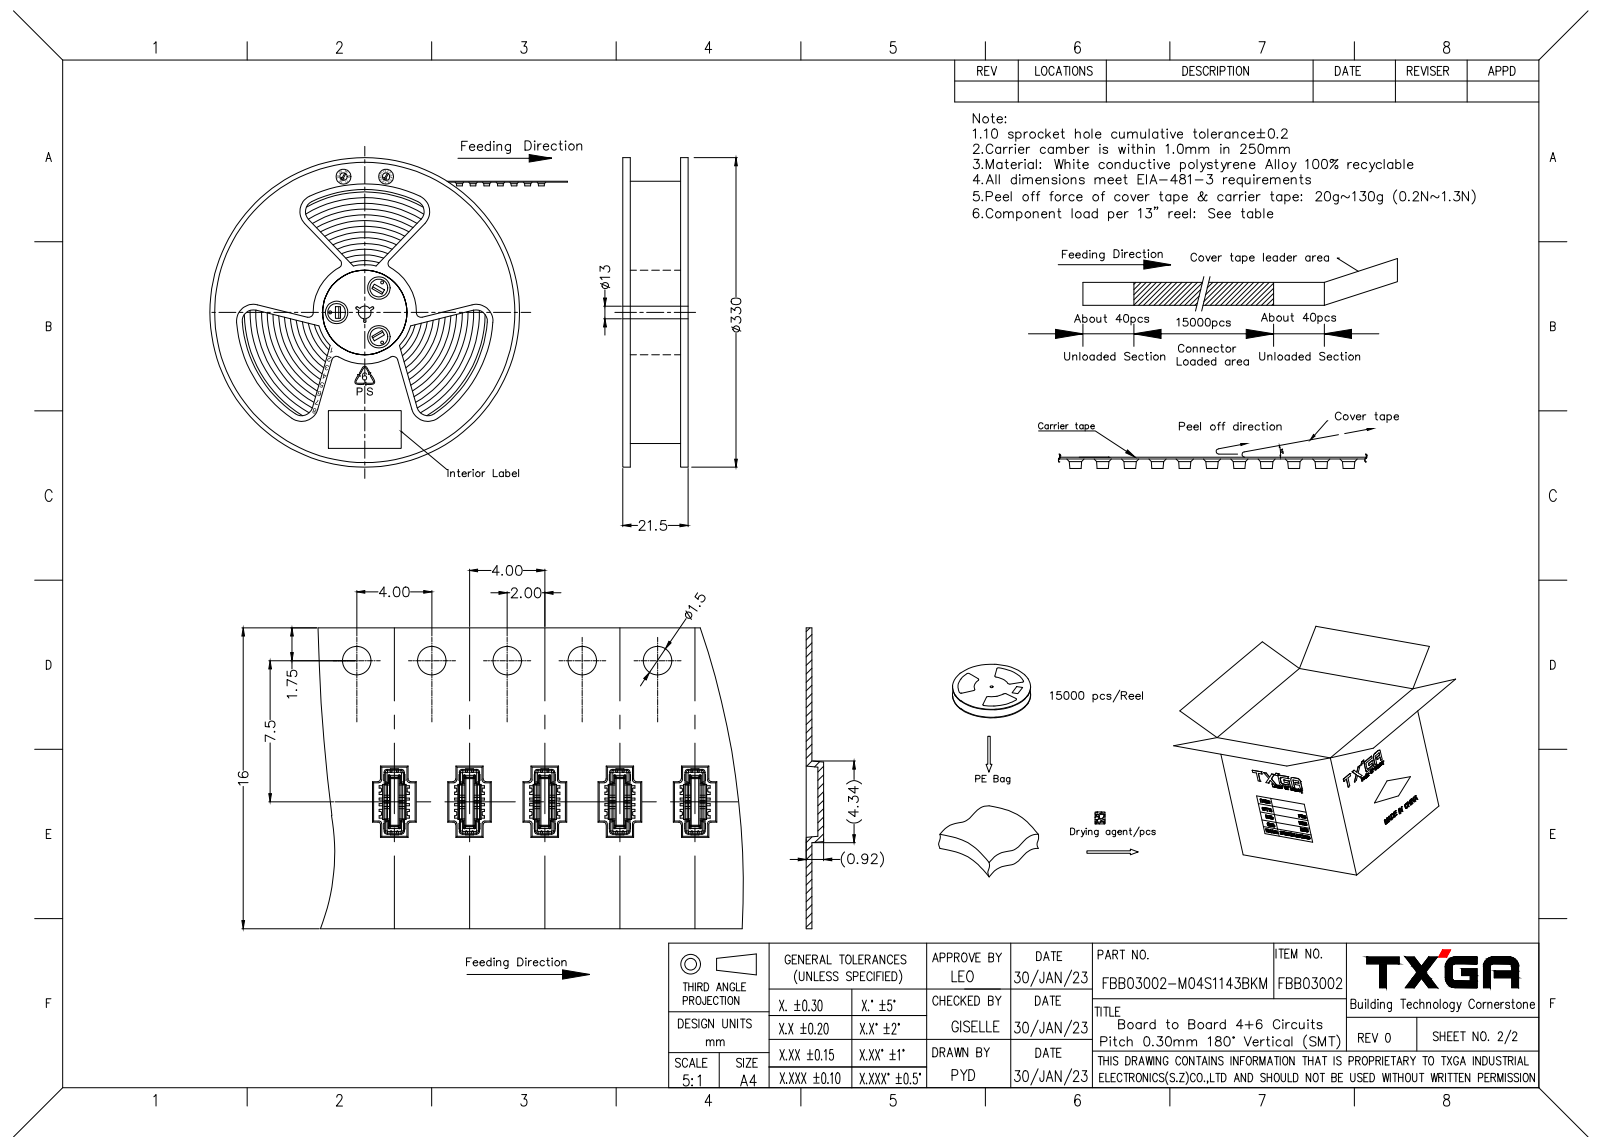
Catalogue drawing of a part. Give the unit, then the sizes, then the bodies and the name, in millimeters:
Units: millimetres
Overall size (bounding box): 3.64 × 1.9 × 0.49
Partial cylindrical surfaces — rounded edges, fillets, slot ends (radius × count): R0.1 ×10, R0.12 ×4, R0.15 ×4, R0.18 ×4, R0.11 ×2
Main face-to-face distances: 0.74, 0.78, 0.52, 1, 0.42, 0.49, 1.04, 0.43, 0.36, 1.06
Volume: 1 mm³ · Surface area: 15 mm²
Bodies: 1 solid, 248 faces (168 planar, 56 cylindrical, 24 other)
Part name (STEP PRODUCT): P
STEP written by: CREO PARAMETRIC BY PTC INC, 2019010 (AUTOMOTIVE_DESIGN)
